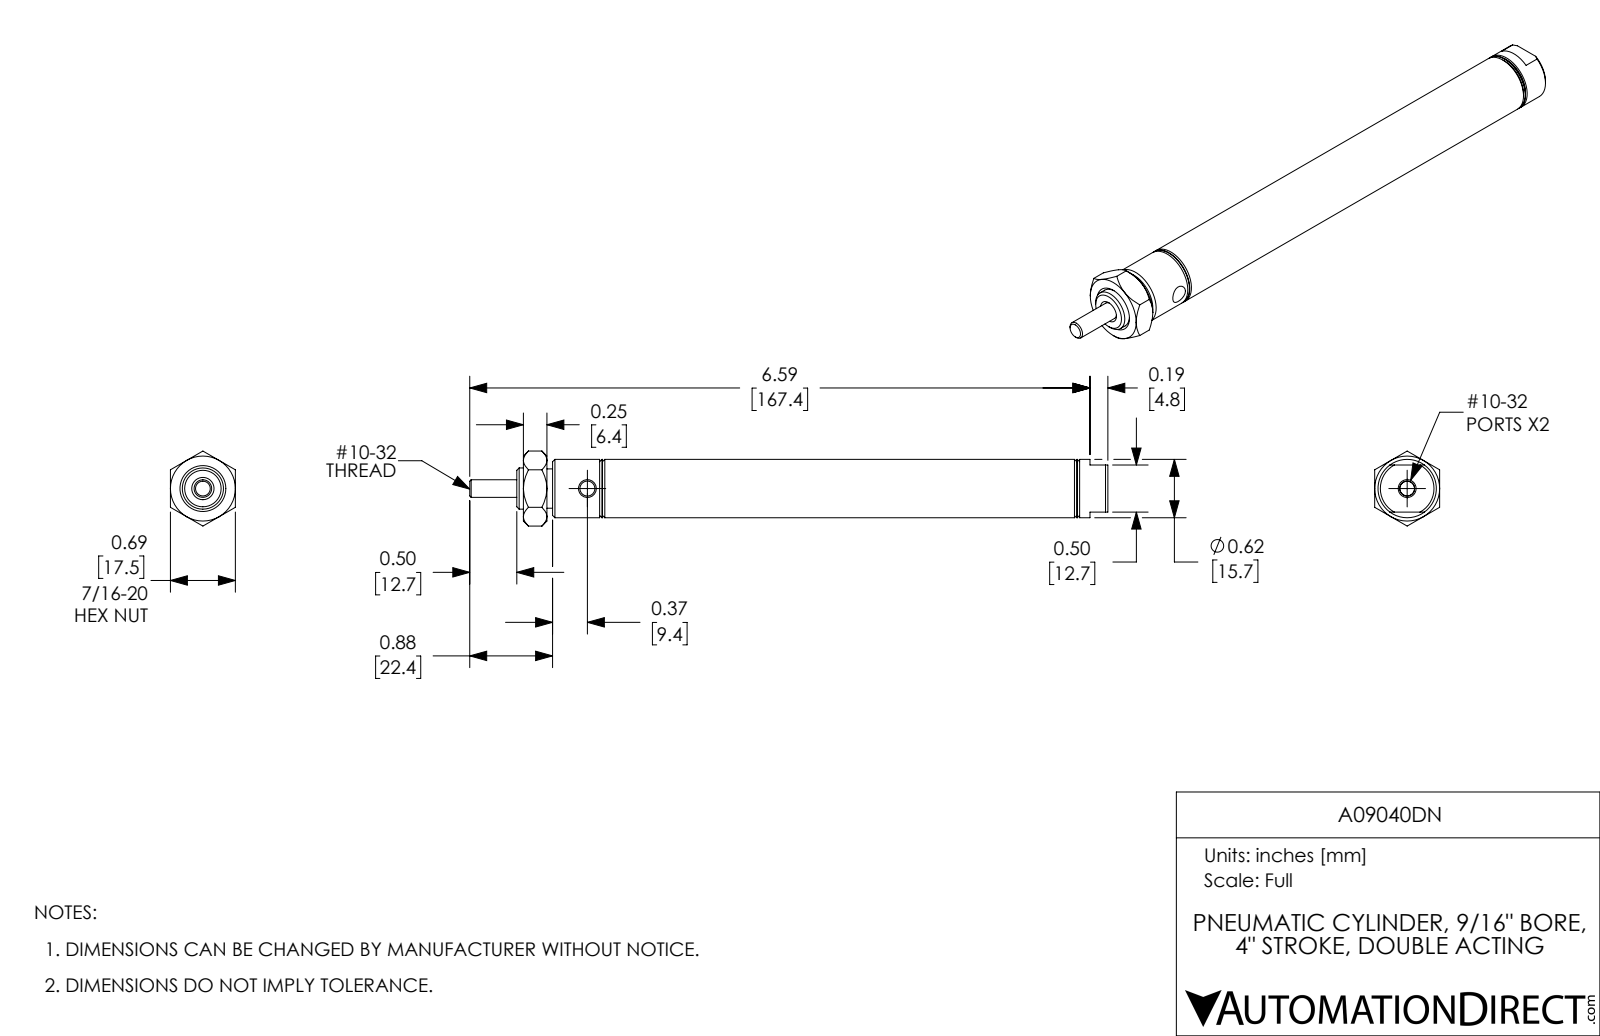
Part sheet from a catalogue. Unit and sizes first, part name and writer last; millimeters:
Units: millimetres
Overall size (bounding box): 172.2 × 20.2 × 17.5
Round holes (diameter × count): ⌀4 ×2, ⌀4.8 ×2, ⌀4 ×1, ⌀4.7 ×1, ⌀11.1 ×1, ⌀14.3 ×1
Round bosses / shafts (diameter × count): ⌀15.7 ×1, ⌀10.6 ×1
Main face-to-face distances: 17.8, 132.1, 12.7, 17.5, 114.3, 151.4, 133.6, 19.3, 30.5, 101.6
Volume: 16 390 mm³ · Surface area: 18 220 mm²
Bodies: 3 solids, 100 faces (28 planar, 34 cylindrical, 38 other)
Part name (STEP PRODUCT): A09040DN; A09040DN_Mounting Nut_D-154; A09040DN-Rod; A09040DN-MainBody
STEP written by: SolidWorks 2017 (AUTOMOTIVE_DESIGN)
